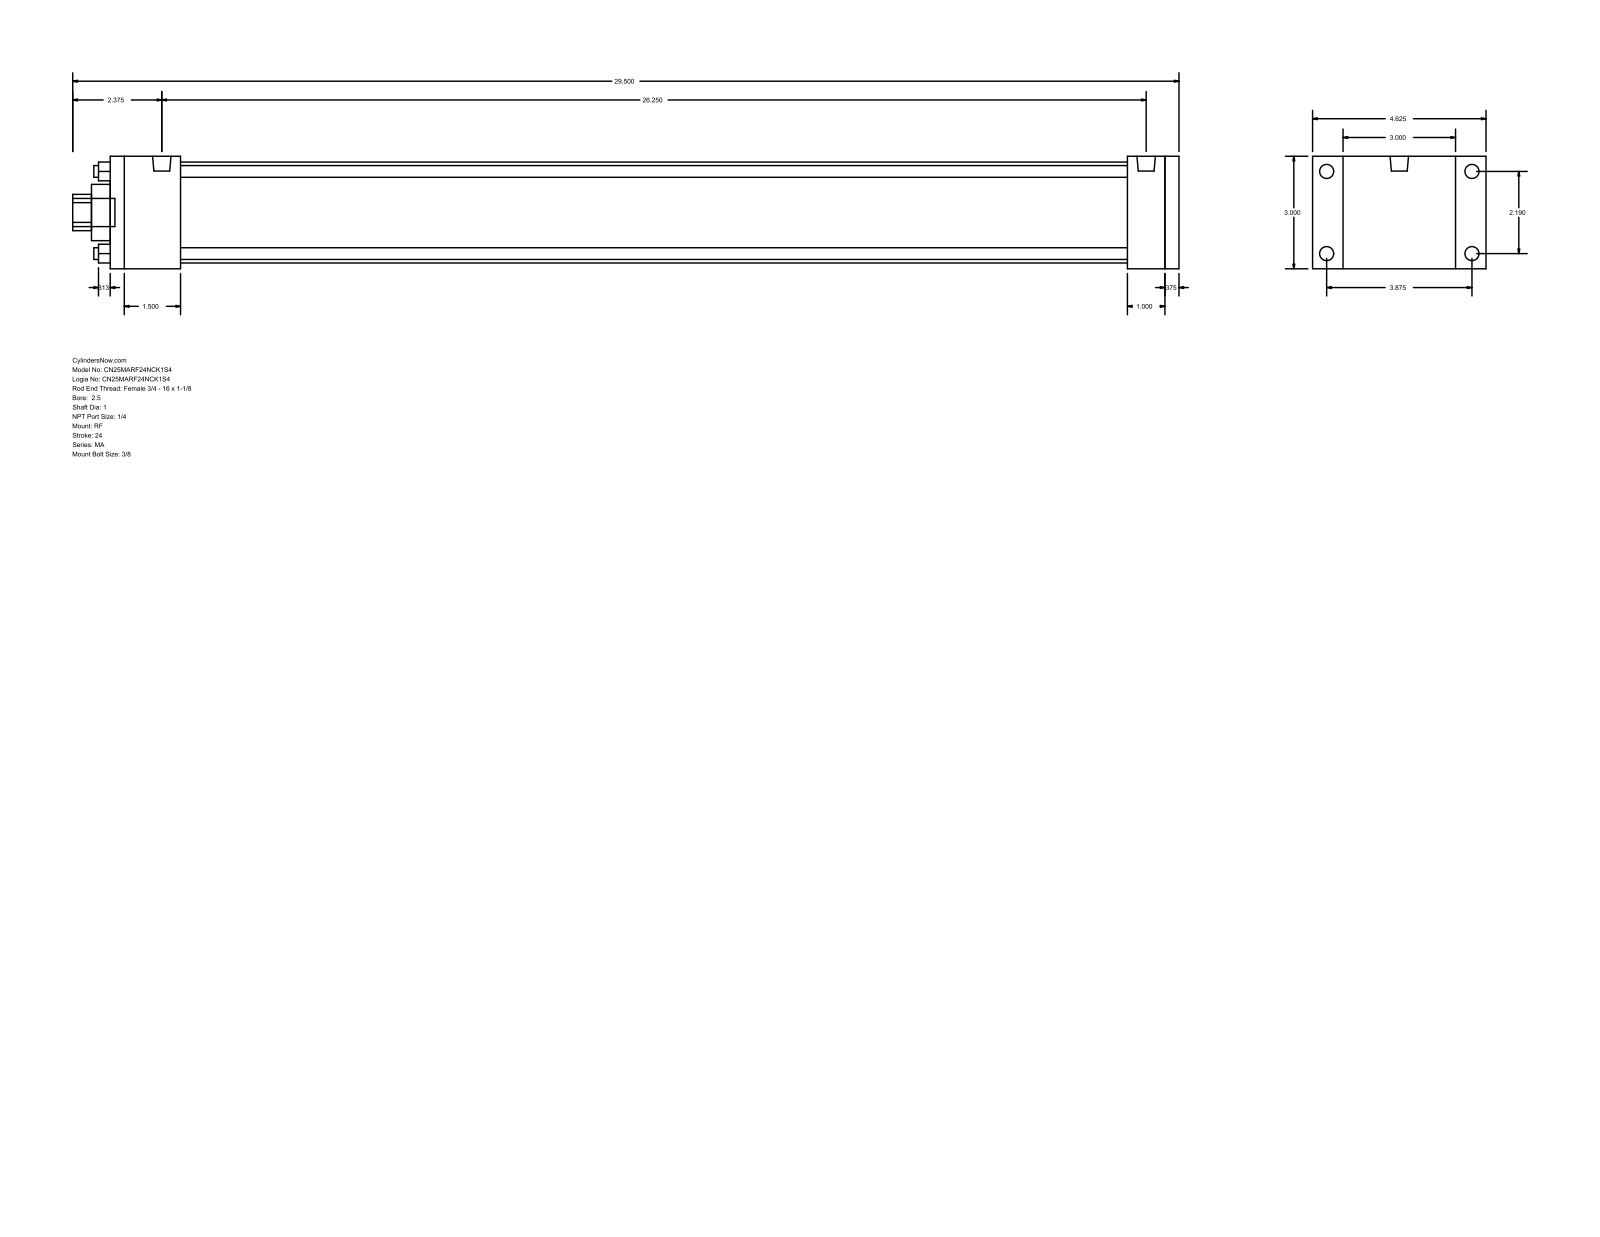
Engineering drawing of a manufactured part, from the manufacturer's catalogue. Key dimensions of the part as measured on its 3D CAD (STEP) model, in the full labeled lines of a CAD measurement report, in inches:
Part name (STEP PRODUCT): MA_RF__0250_1
STEP written by: GSSL Pune (CONFIG_CONTROL_DESIGN)
Units: inches
Bodies: 0 solids, 92 faces (64 planar, 28 cylindrical, 0 other)
Overall size (bounding box): 29.5 × 4.625 × 3
Round holes (diameter × count): ⌀0.313 ×4, ⌀1 ×1, ⌀1.5 ×1, ⌀2.69 ×1
Round bosses / shafts (diameter × count): ⌀0.375 ×4, ⌀0.313 ×4, ⌀0.492 ×2, ⌀0.75 ×1
Partial cylindrical surfaces — rounded edges, fillets, slot ends (radius × count): R0.484 ×1
Main face-to-face distances: 3, 28.5, 0.375, 28.125, 1.875, 27.125, 25.25, 26.25, 26.625, 1
Hole centre spacings: 1.548, 2.19, 3.097
